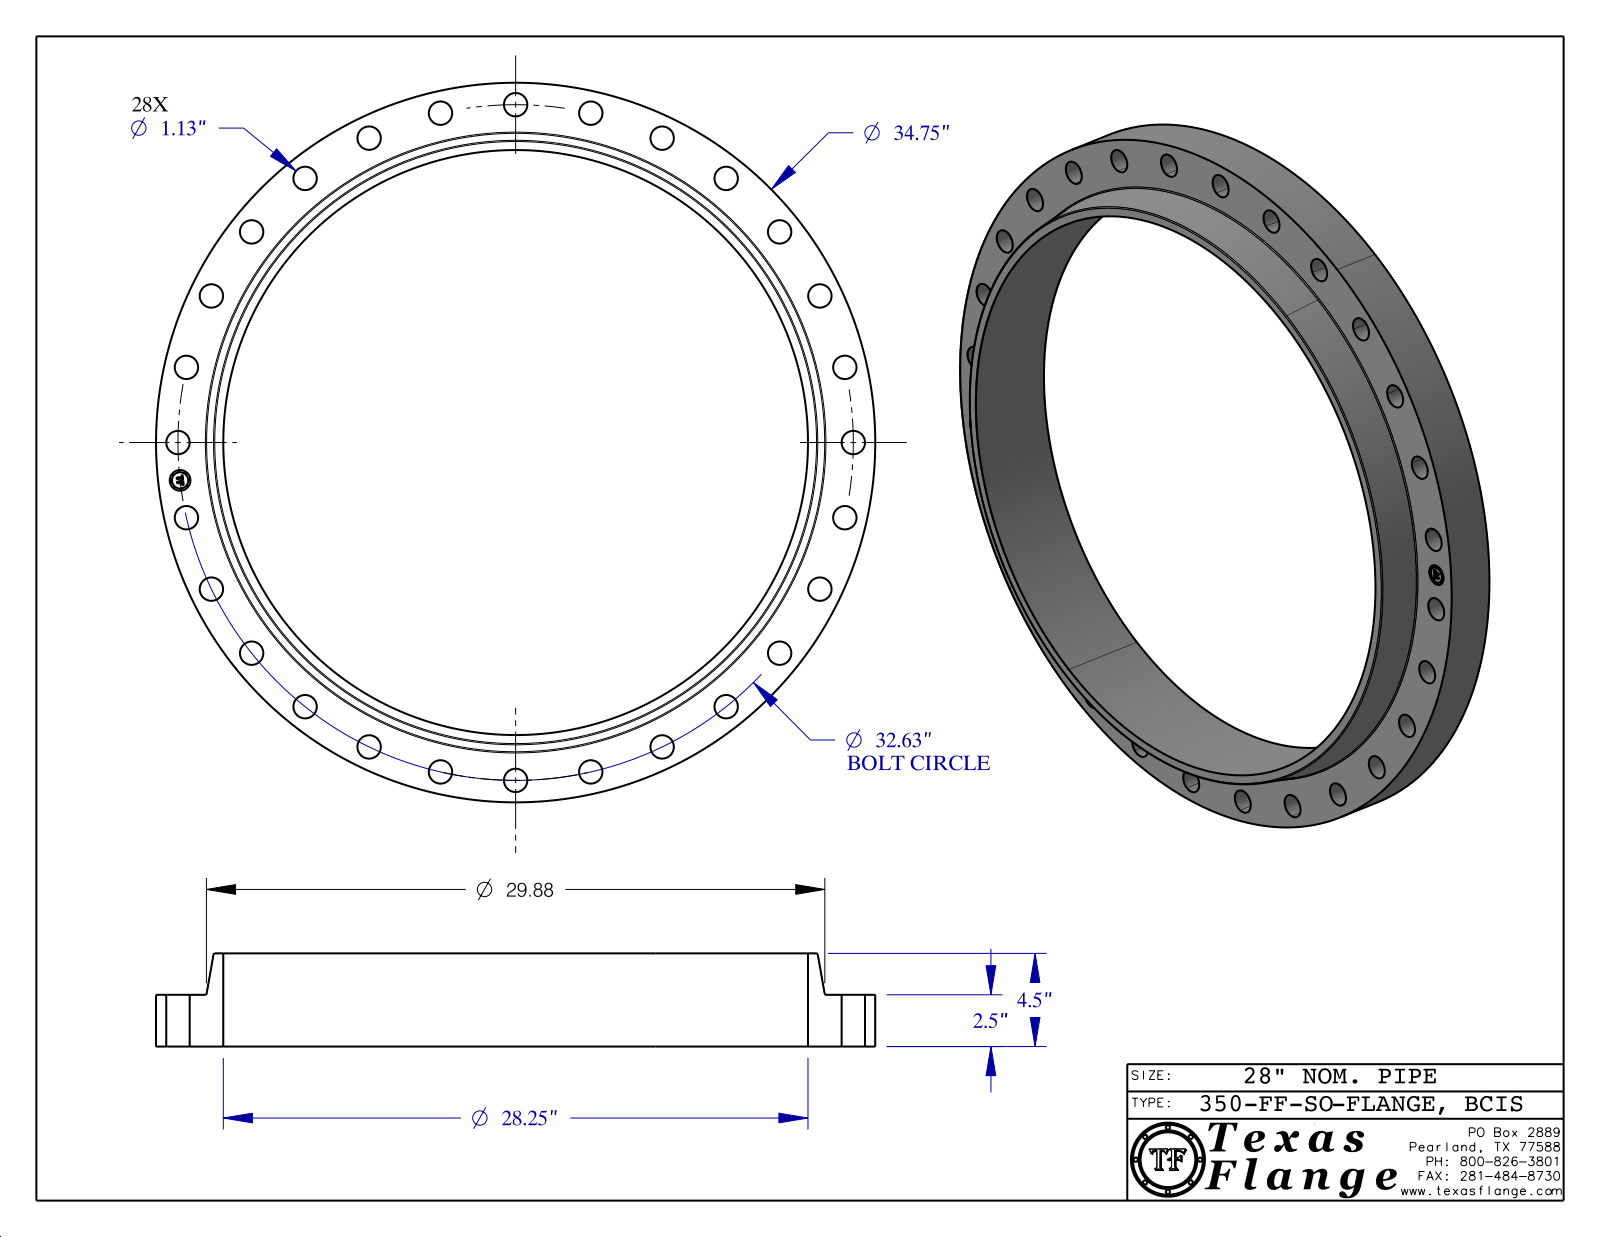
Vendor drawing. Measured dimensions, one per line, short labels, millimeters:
name: BCIS, Class 350-FF-SO
written by: CATIA V5 STEP AP214 (AUTOMOTIVE_DESIGN)
unit: mm
bodies: 1 solid, 454 faces (368 planar, 80 cylindrical, 6 other)
size: 882.7 × 882.7 × 114.3
volume: 13 930 000 mm³; area: 1 072 000 mm²
holes: 28× ⌀28.7, 1× ⌀25.4, 1× ⌀717.6
bosses: 8× ⌀1.5, 1× ⌀882.7, 1× ⌀20
face distances: 63.5, 114.3, 50.8, 0.4, 63.1, 51.2, 7.6, 7.4, 1.4, 4.9
hole spacings: 359.6, 414.4, 586.1, 648, 701.8, 746.7, 516.7, 184.4
